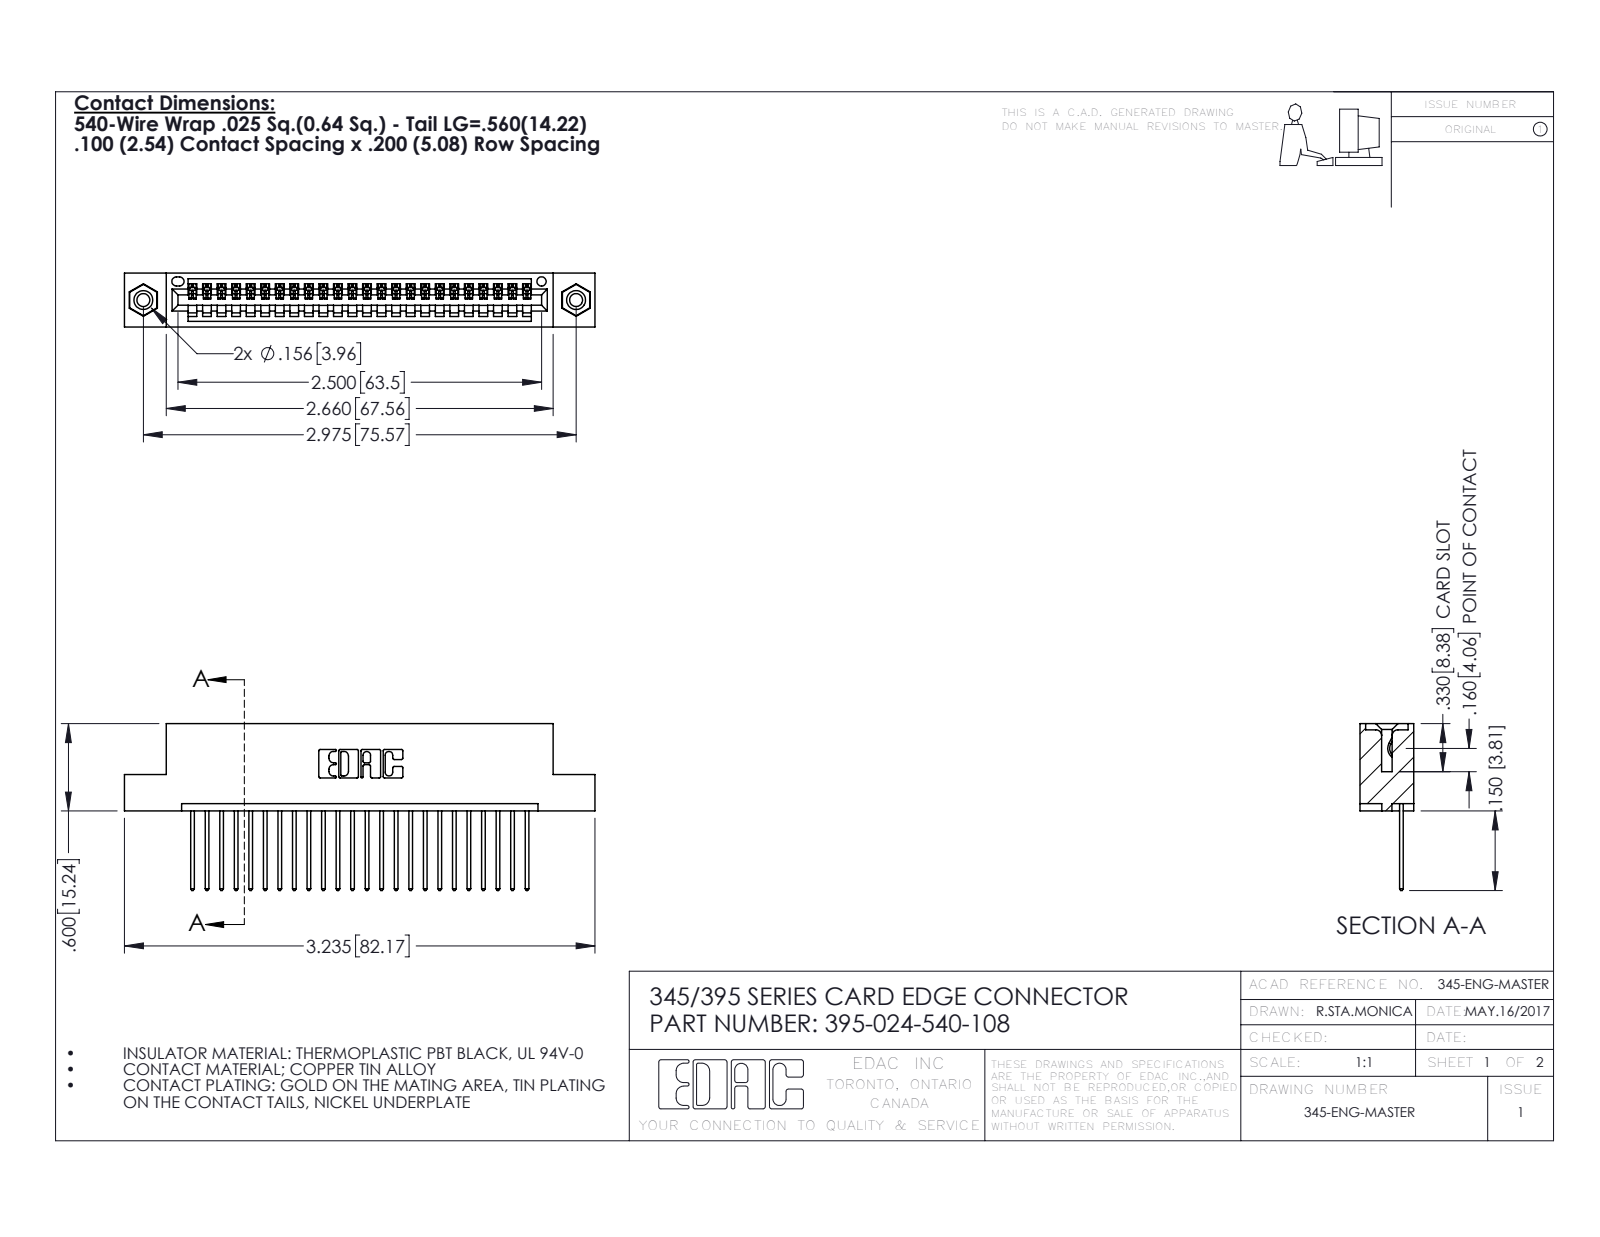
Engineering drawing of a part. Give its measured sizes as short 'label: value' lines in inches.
name: 345-250-001_345-250-003-102; 345-292-001_345-293-140; 345 Part_Flush Mounting Lugs - 0.156 Dia-TI; 395-024-540-108
written by: SolidWorks 2016 (CONFIG_CONTROL_DESIGN)
unit: in
bodies: 27 solids, 1578 faces (1072 planar, 490 cylindrical, 16 other)
size: 3.235 × 1.147 × 0.37
volume: 0.469 in³; area: 15.84 in²
holes: 2× ⌀0.089, 2× ⌀0.125, 2× ⌀0.156, 1× ⌀0.064
bosses: 2× ⌀0.155
rounds: 48× R0.006, 48× R0.01, 22× R0.01, 6× R0.007, 6× R0.031, 3× R0.026, 2× R0.031, 2× R0.04
face distances: 0.072, 0.298, 0.2, 0.37, 0.098, 0.272, 0.025, 0.225, 0.149, 0.072
hole spacings: 0.27, 2.741, 2.975
